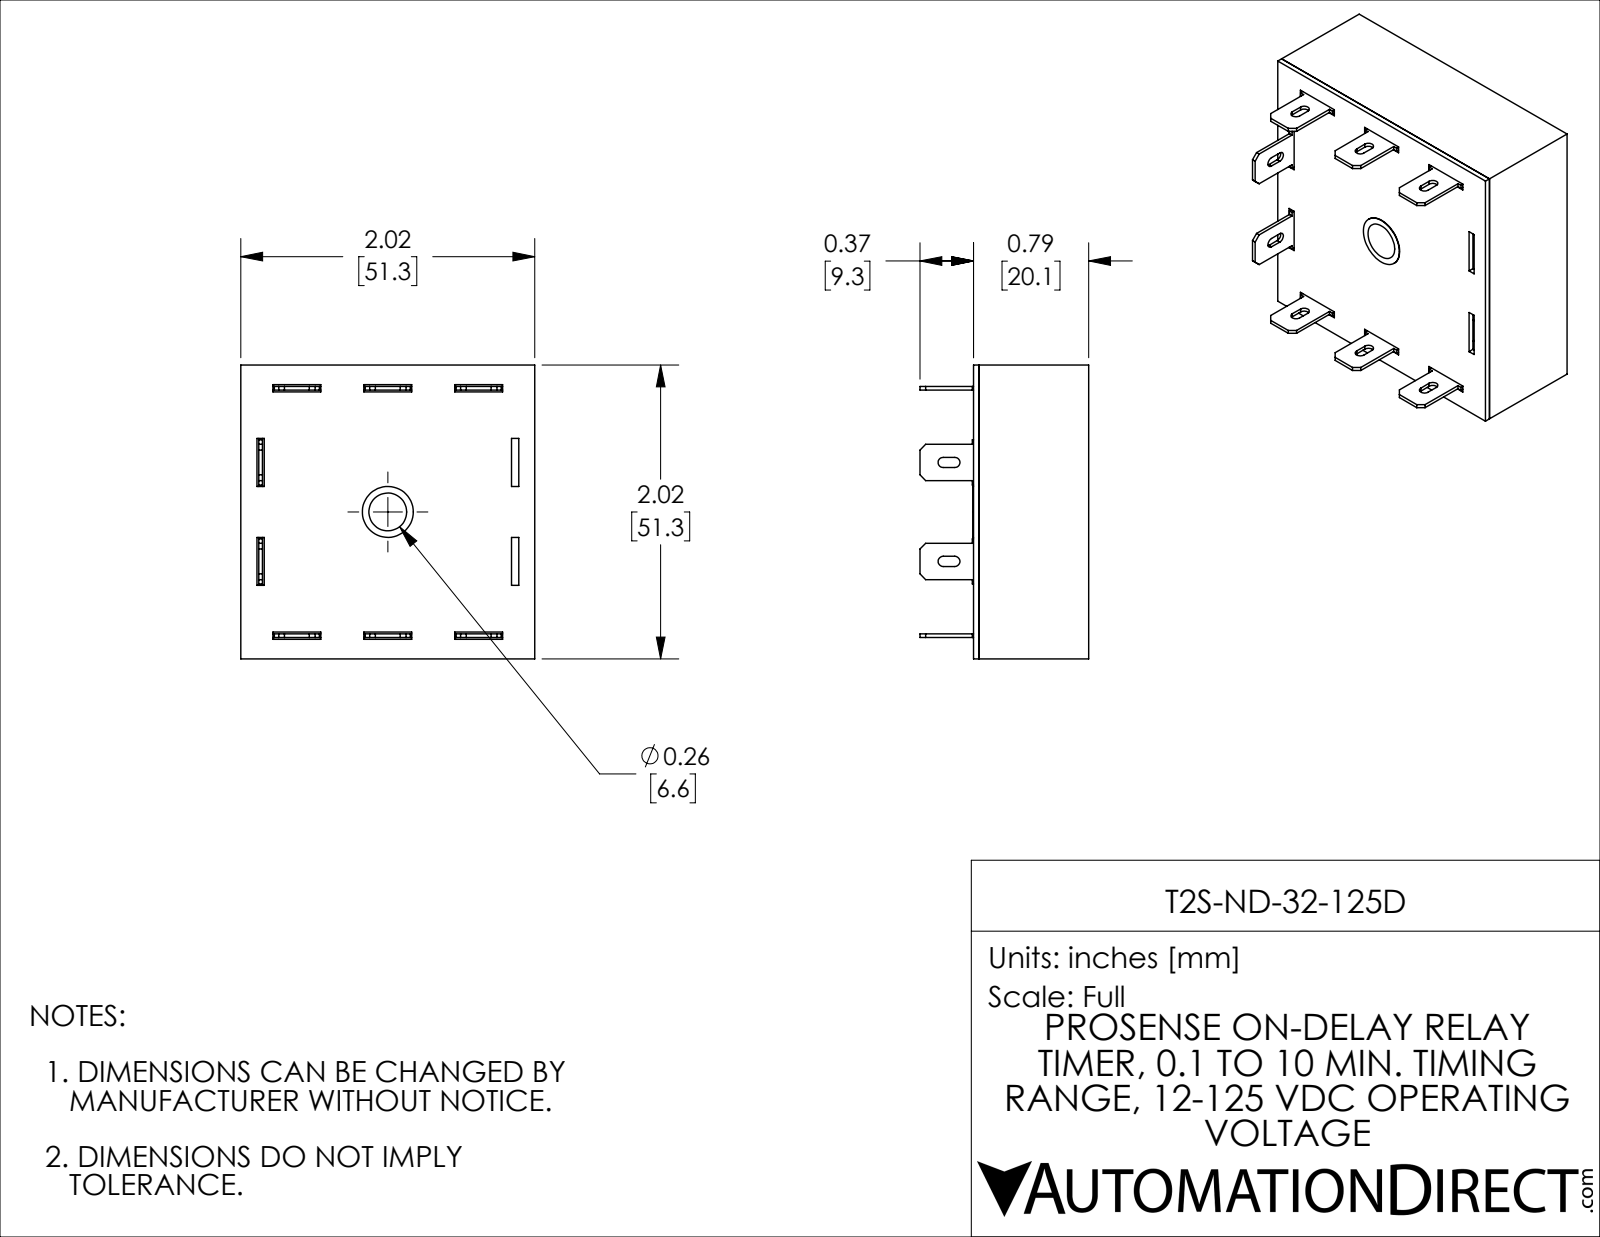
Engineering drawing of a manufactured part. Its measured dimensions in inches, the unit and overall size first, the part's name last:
Units: inches
Overall size (bounding box): 2.02 × 2.02 × 1.16
Round holes (diameter × count): ⌀0.35 ×1
Partial cylindrical surfaces — rounded edges, fillets, slot ends (radius × count): R0.035 ×10
Main face-to-face distances: 0.045, 1.975, 0.754, 0.792, 0.038, 0.709, 0.747, 2.02, 1.93, 0.147
Volume: 0.674 in³ · Surface area: 35.37 in²
Bodies: 10 solids, 256 faces (234 planar, 20 cylindrical, 2 other)
Part name (STEP PRODUCT): T2S-ND-32-125D
STEP written by: SolidWorks 2021 (CONFIG_CONTROL_DESIGN)
